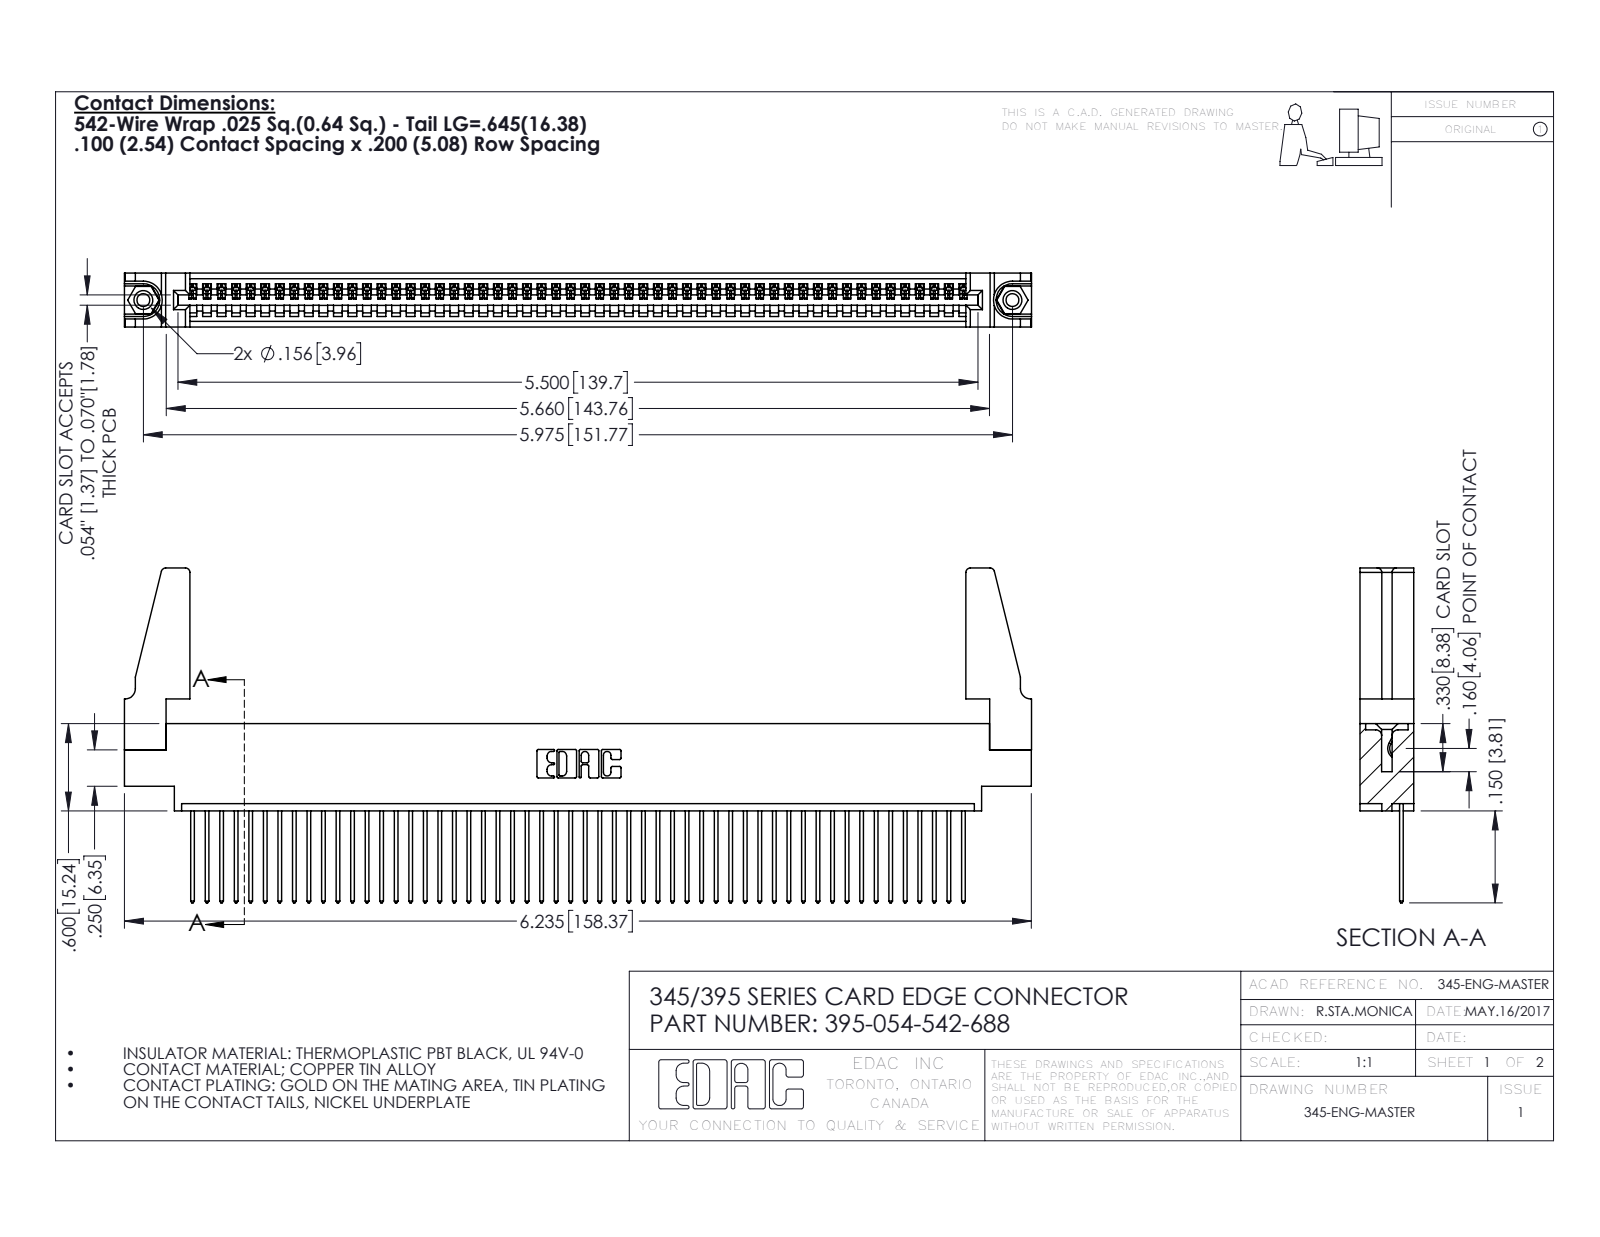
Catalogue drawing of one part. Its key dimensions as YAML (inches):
part_name: "345-292-001_345-293-142; 345-250-001_345-250-001-102; 395-054-542-688; 345 Part_0.170 Offset - 0.156 Dia-TH (+1 more)"
step_written_by: "SolidWorks 2016 (CONFIG_CONTROL_DESIGN)"
units: inches
bodies: {solids: 59, faces: 3386, planar: 2316, cylindrical: 1054, other: 16}
overall_size: [6.236, 2.302, 0.37]
volume: 1.123
surface_area: 37.68
round_holes:
  - {diameter: 0.089, count: 2}
  - {diameter: 0.125, count: 2}
  - {diameter: 0.156, count: 2}
  - {diameter: 0.064, count: 1}
round_bosses_or_shafts:
  - {diameter: 0.155, count: 2}
partial_cylinders:
  - {radius: 0.006, count: 108}
  - {radius: 0.01, count: 108}
  - {radius: 0.01, count: 22}
  - {radius: 0.03, count: 8}
  - {radius: 0.007, count: 6}
  - {radius: 0.031, count: 6}
  - {radius: 0.026, count: 3}
  - {radius: 0.031, count: 2}
face_to_face_distances: [0.072, 0.298, 0.37, 0.098, 0.272, 0.025, 0.2, 0.225, 0.175, 0.149]
hole_center_spacings: [0.27, 5.739, 5.975]
